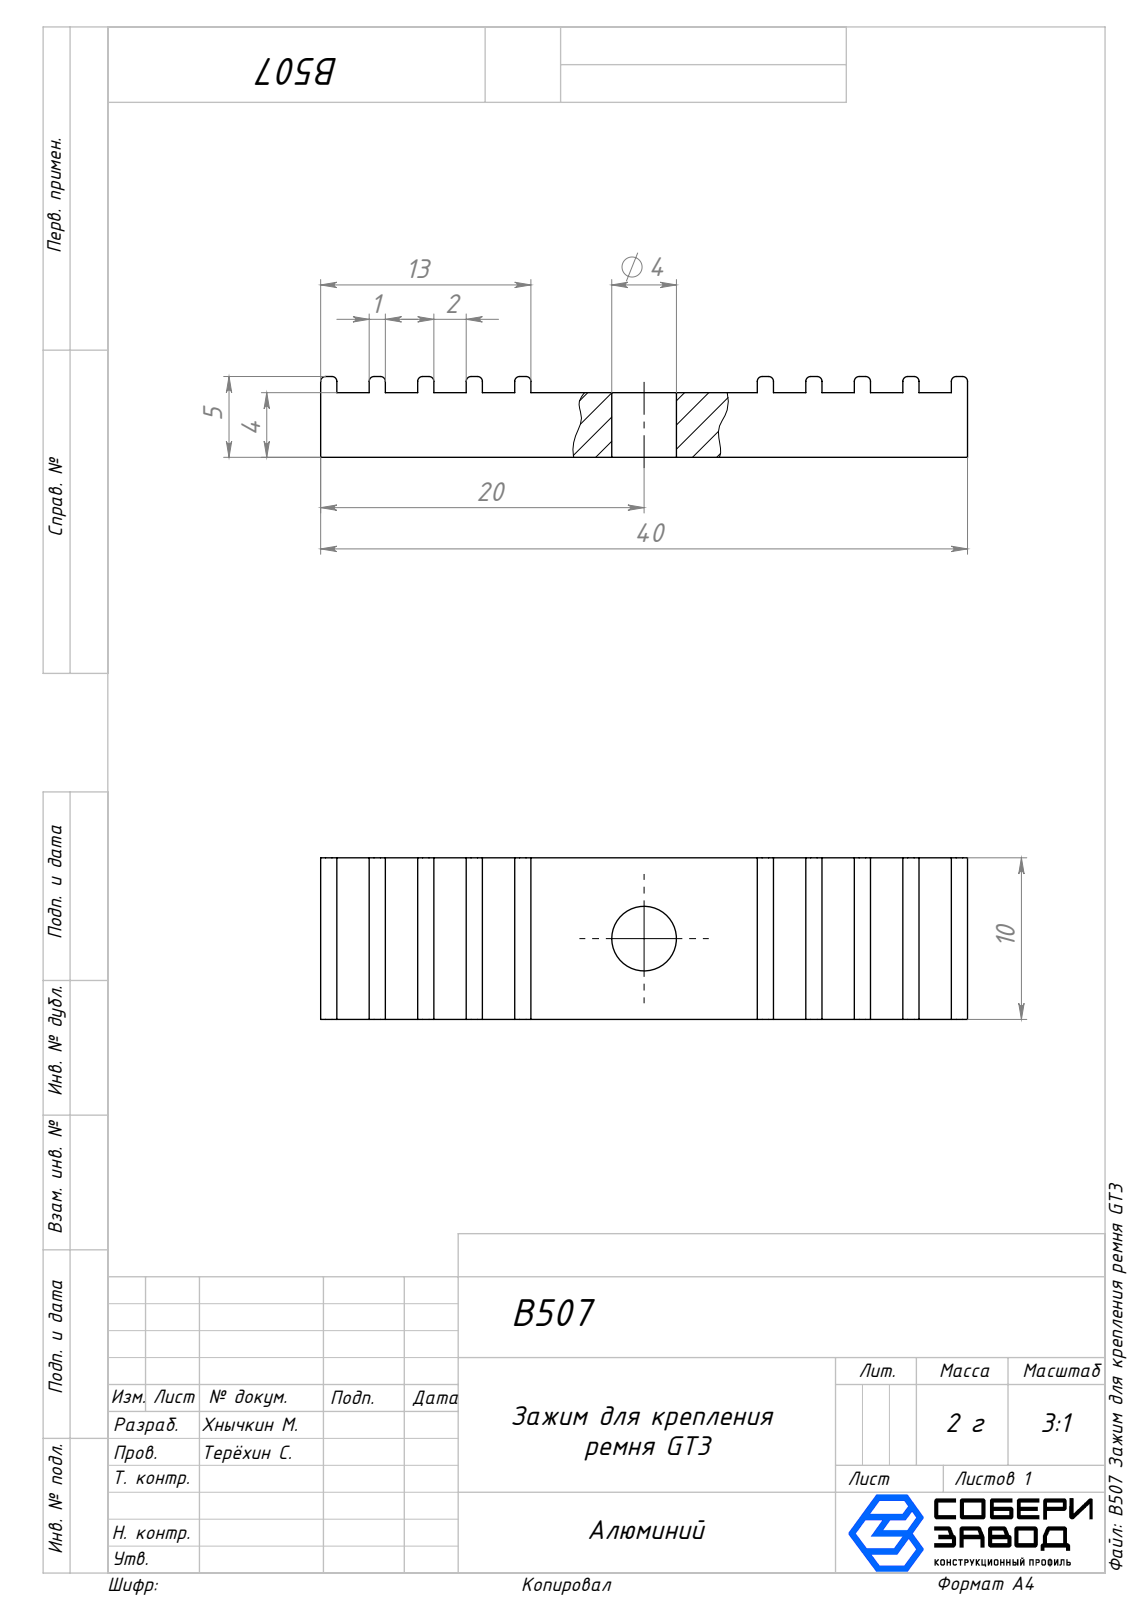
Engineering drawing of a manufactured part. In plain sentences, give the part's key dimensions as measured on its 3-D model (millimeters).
The part is named "B507 Зажим для крепления ремня GT3". Its 3-D file was written by "SolidWorks 2025 (AUTOMOTIVE_DESIGN)". It is 1 solid with 64 faces: 42 planar, 22 cylindrical and 0 other. Overall it measures 40 by 10 by 5 millimeters. Its volume is 1 646 cubic millimeters and its surface area 1 419 square millimeters. Round holes: 1 of diameter 4. Partial cylindrical surfaces (rounded edges, fillets, slot ends): 20 of radius 0.3. The main face-to-face distances are 4, 10, 3, 1, 6, 5, 27, 9, 2, 30.
